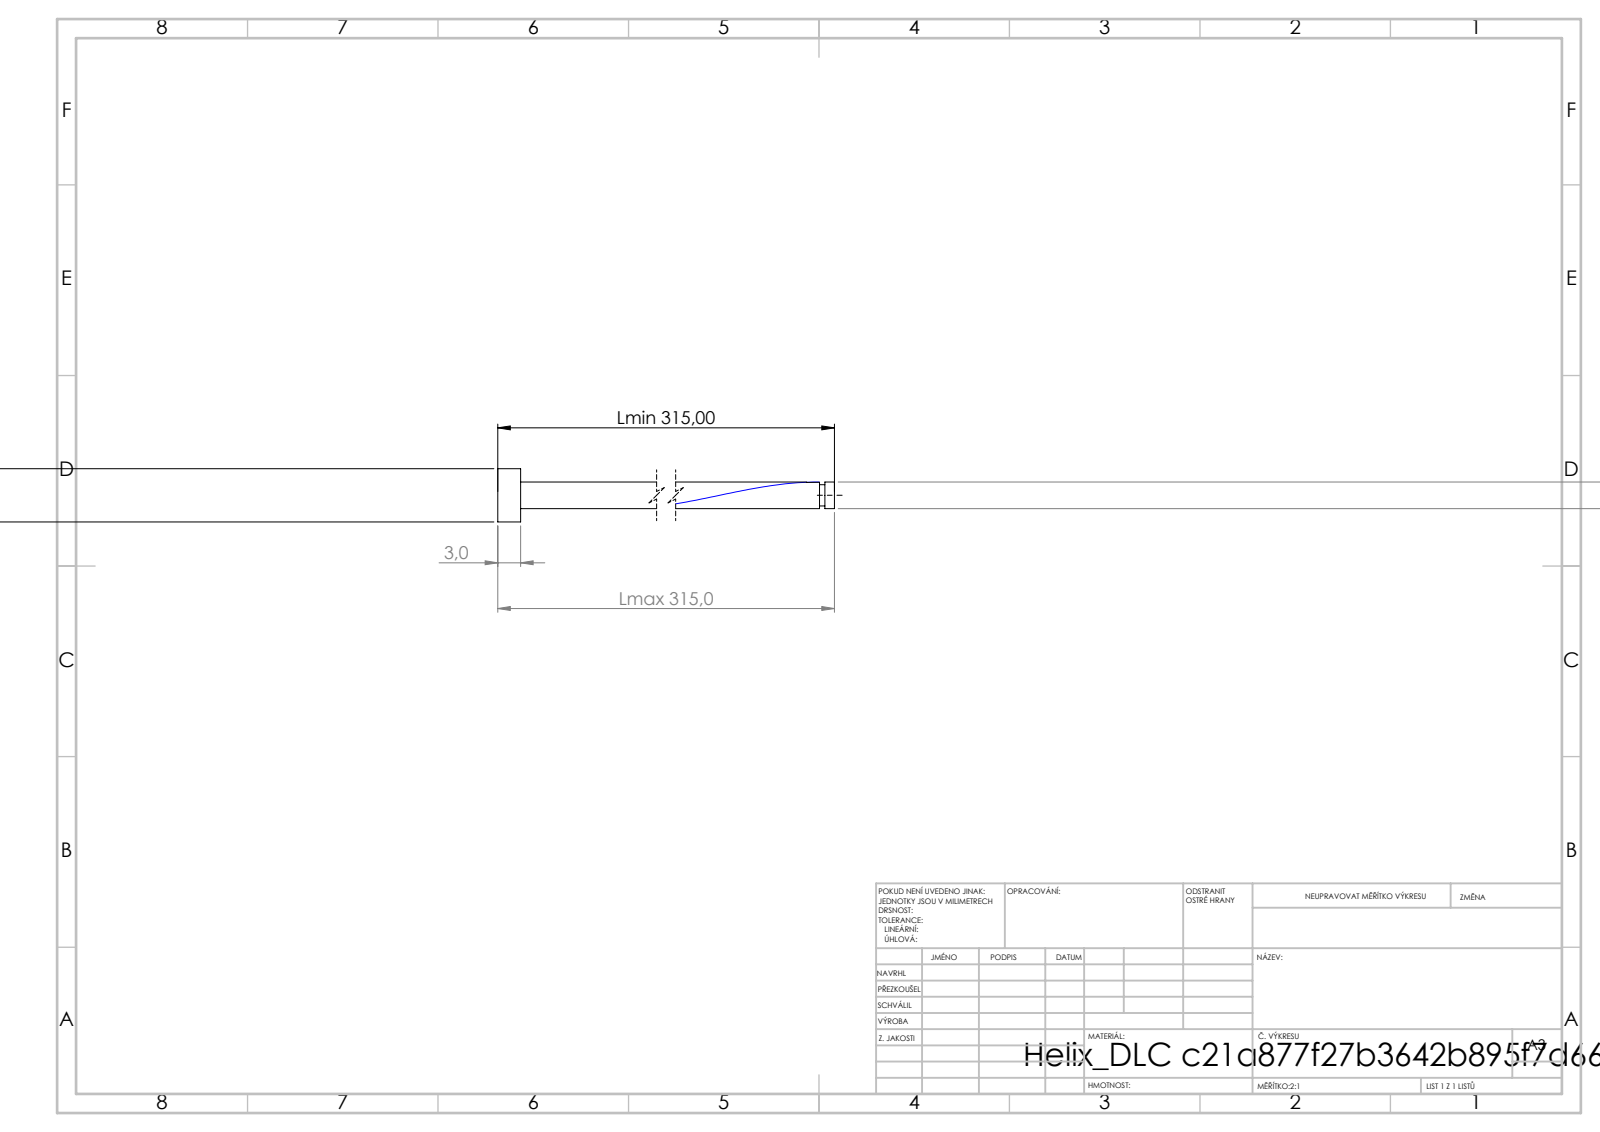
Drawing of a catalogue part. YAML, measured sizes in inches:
step_written_by: "SolidWorks 2019 (CONFIG_CONTROL_DESIGN)"
units: inches
bodies: {solids: 1, faces: 16, planar: 6, cylindrical: 9, other: 1}
overall_size: [12.402, 0.276, 0.276]
volume: 0.229
surface_area: 7.42
round_bosses_or_shafts:
  - {diameter: 0.276, count: 1}
  - {diameter: 0.138, count: 1}
  - {diameter: 0.11, count: 1}
face_to_face_distances: [0.118, 12.402, 12.283, 12.352, 12.234, 0.05, 12.324, 12.206, 0.028, 0.077]
